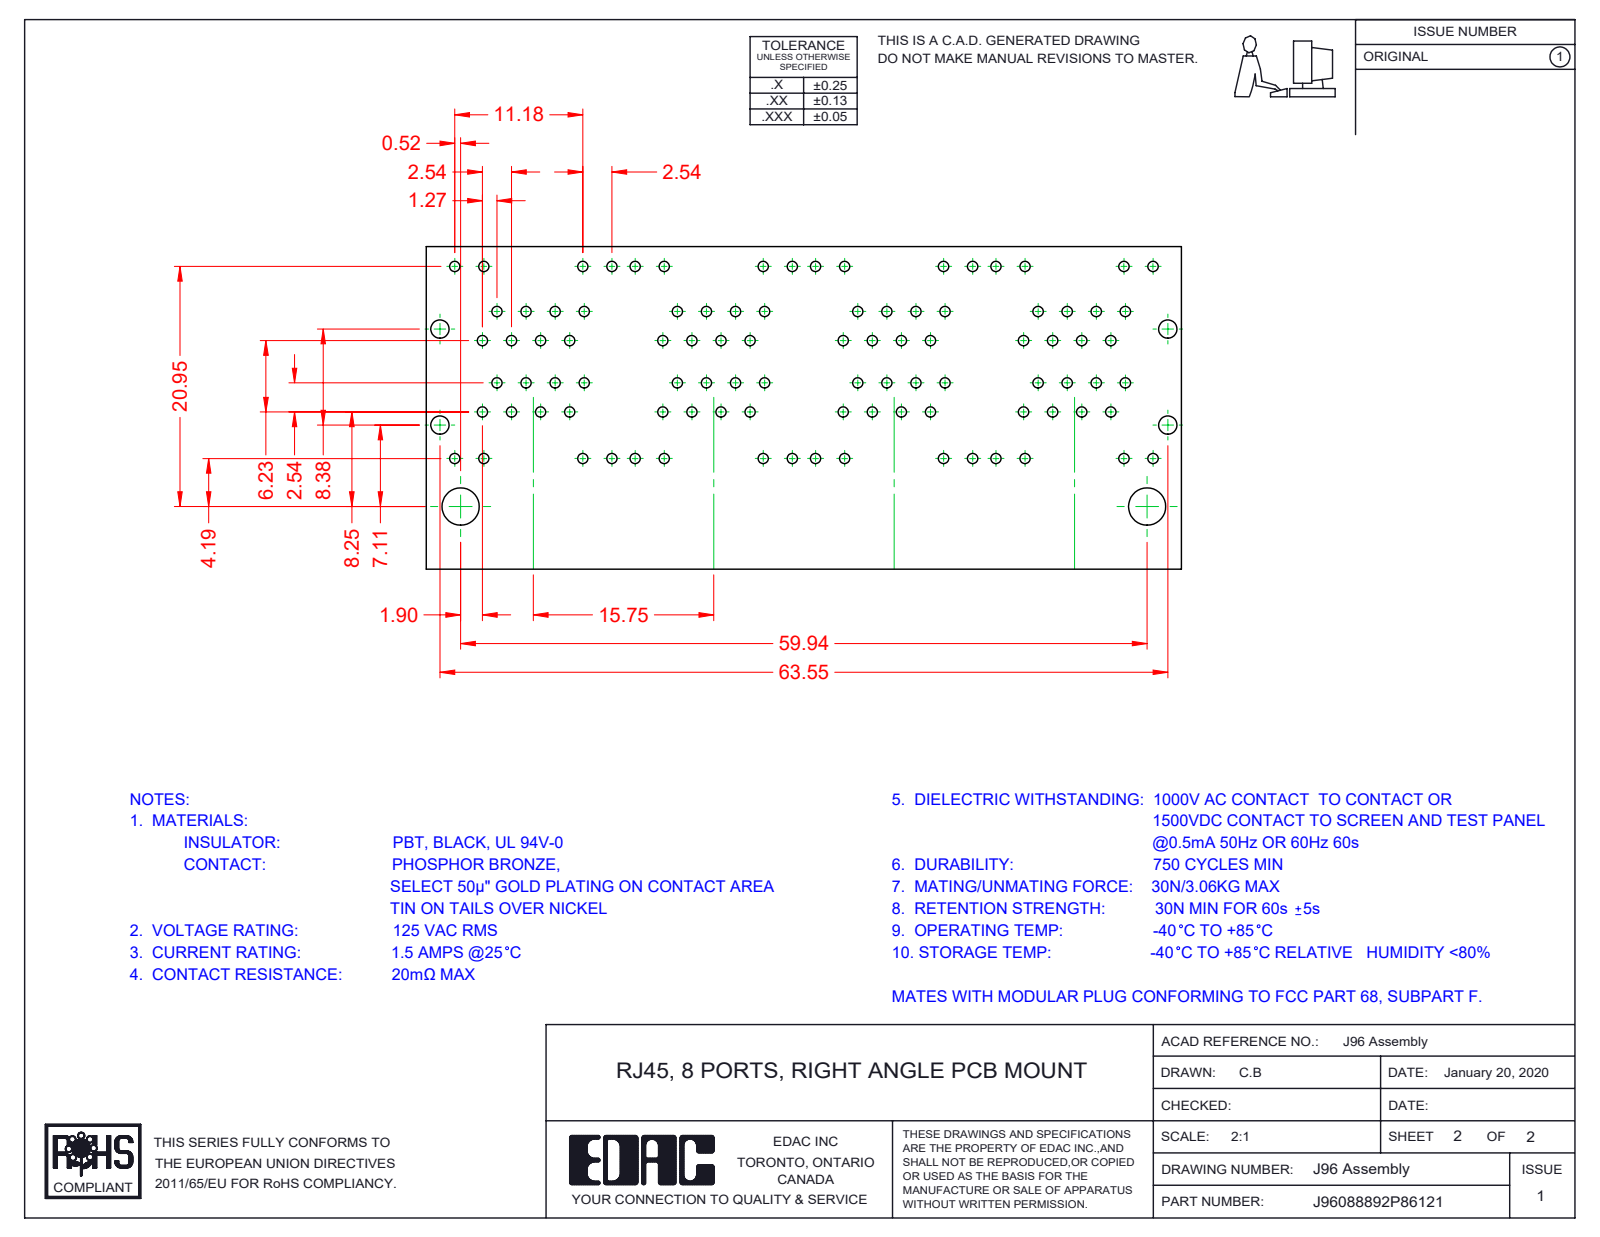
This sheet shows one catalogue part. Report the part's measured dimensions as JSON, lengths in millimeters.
{"part_name": "96 LED RH Lower_6-Red-Green; 96 Contacts Upper; 96 LED LH Upper_8-Red-Yellow; 96 Insulator_8 Ports (+8 more)", "step_written_by": "SolidWorks 2016 (CONFIG_CONTROL_DESIGN)", "units": "millimeters", "bodies": {"solids": 96, "faces": 7674, "planar": 6069, "cylindrical": 1339, "other": 266}, "overall_size": [64.05, 29.58, 28.68], "volume_mm3": 24160, "surface_area_mm2": 63658, "round_holes": [[1.7, 3]], "round_bosses_or_shafts": [[1.68, 3]], "partial_cylinders_radius": [[0.25, 124], [0.35, 73], [1, 72], [0.5, 49], [0.91, 32], [0.2, 21], [0.7, 11], [0.22, 8]], "face_to_face_distances": [15.75, 0.35, 9.95, 1.17, 1.6, 0.54, 9.98, 10.18, 12.67, 3.37], "hole_center_spacings": [15.75, 31.5]}
